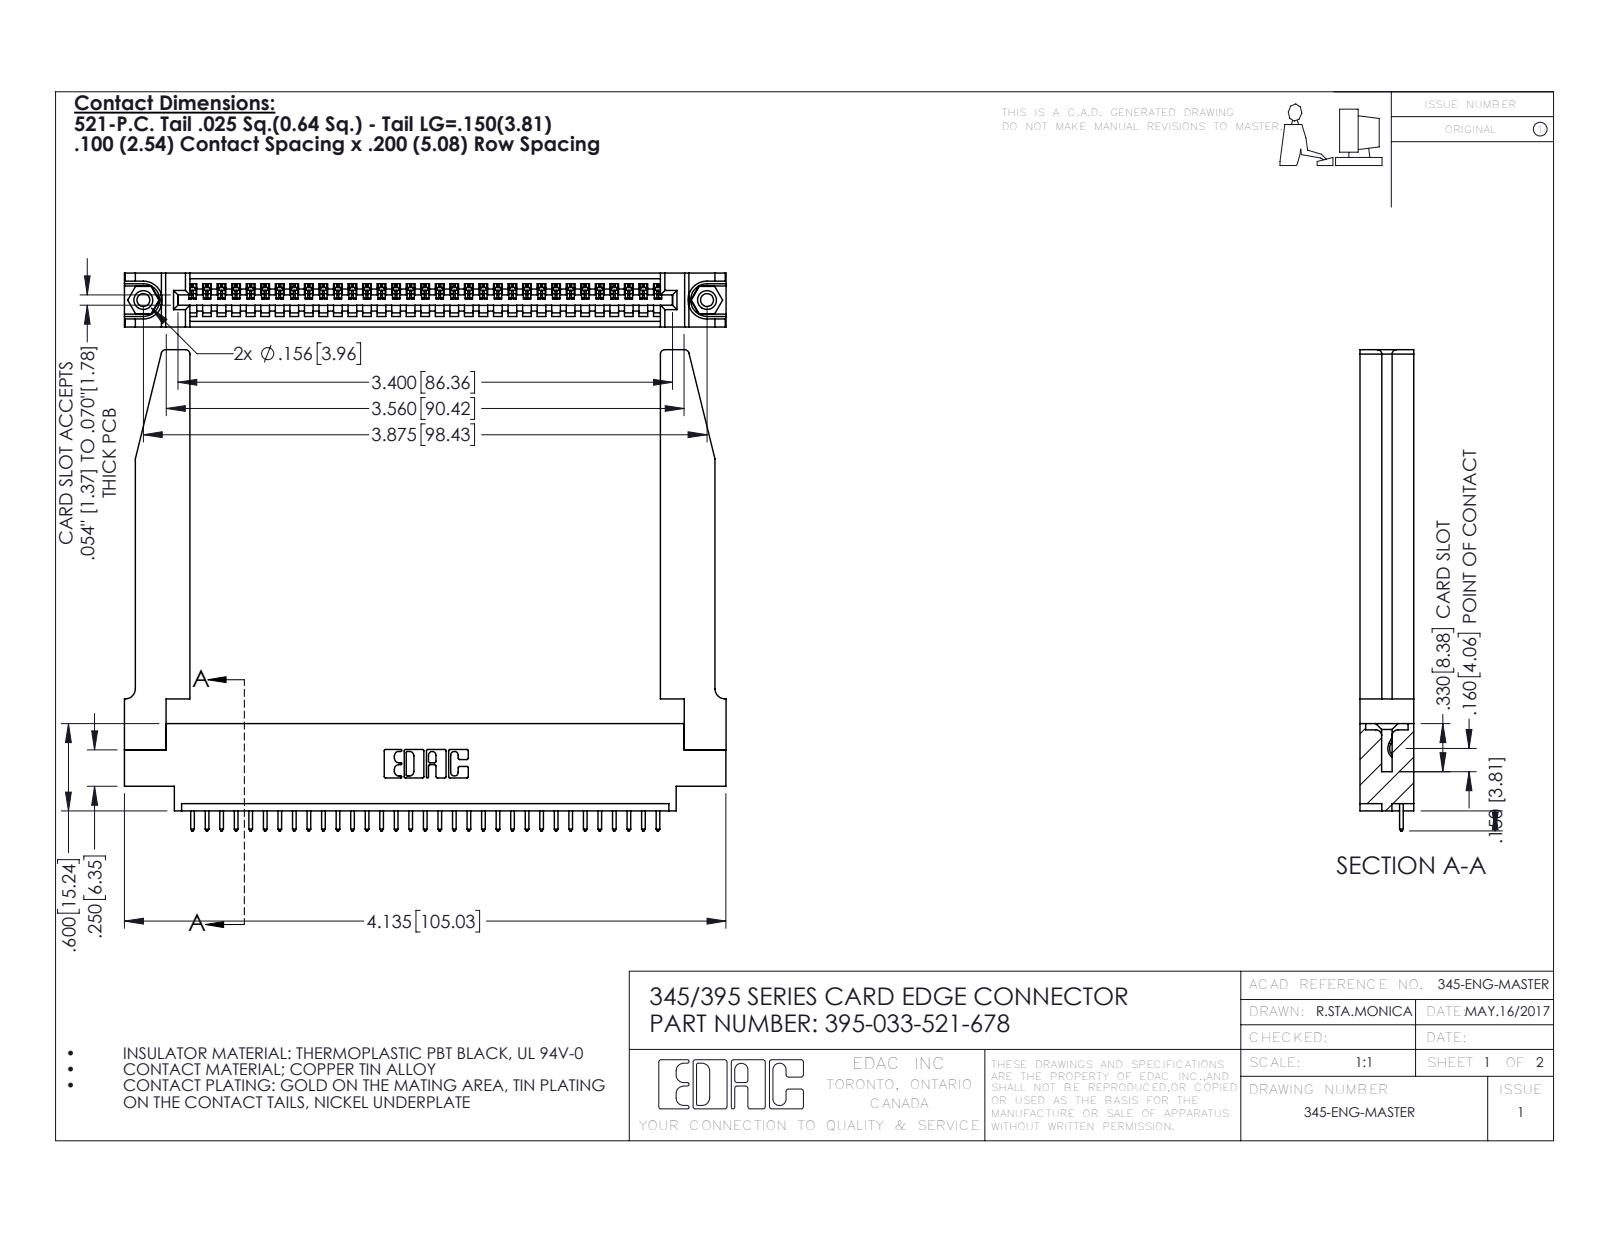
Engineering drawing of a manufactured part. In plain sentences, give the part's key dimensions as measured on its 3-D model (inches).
The part is named "345-292-001_345-293-121; 345 Part_0.170 Offset - 0.156 Dia-TH; 345-220-078_345-220-078; 395-033-521-678 (+1 more)". Its 3-D file was written by "SolidWorks 2016 (CONFIG_CONTROL_DESIGN)". It is 38 solids with 2278 faces: 1546 planar, 680 cylindrical and 52 other. Overall it measures 4.136 by 3.307 by 0.37 inches. Its volume is 1.066 cubic inches and its surface area 30.02 square inches. Round holes: 2 of diameter 0.089, 2 of diameter 0.125, 2 of diameter 0.156, 1 of diameter 0.064. Round bosses or shafts: 2 of diameter 0.155. Partial cylindrical surfaces (rounded edges, fillets, slot ends): 66 of radius 0.006, 66 of radius 0.01, 22 of radius 0.01, 8 of radius 0.03, 6 of radius 0.007, 6 of radius 0.031, 3 of radius 0.026, 2 of radius 0.031. The main face-to-face distances are 0.37, 0.072, 0.298, 0.098, 0.272, 0.025, 0.2, 0.148, 0.15, 0.225. The hole center spacings are 0.27, 3.64, 3.875.
